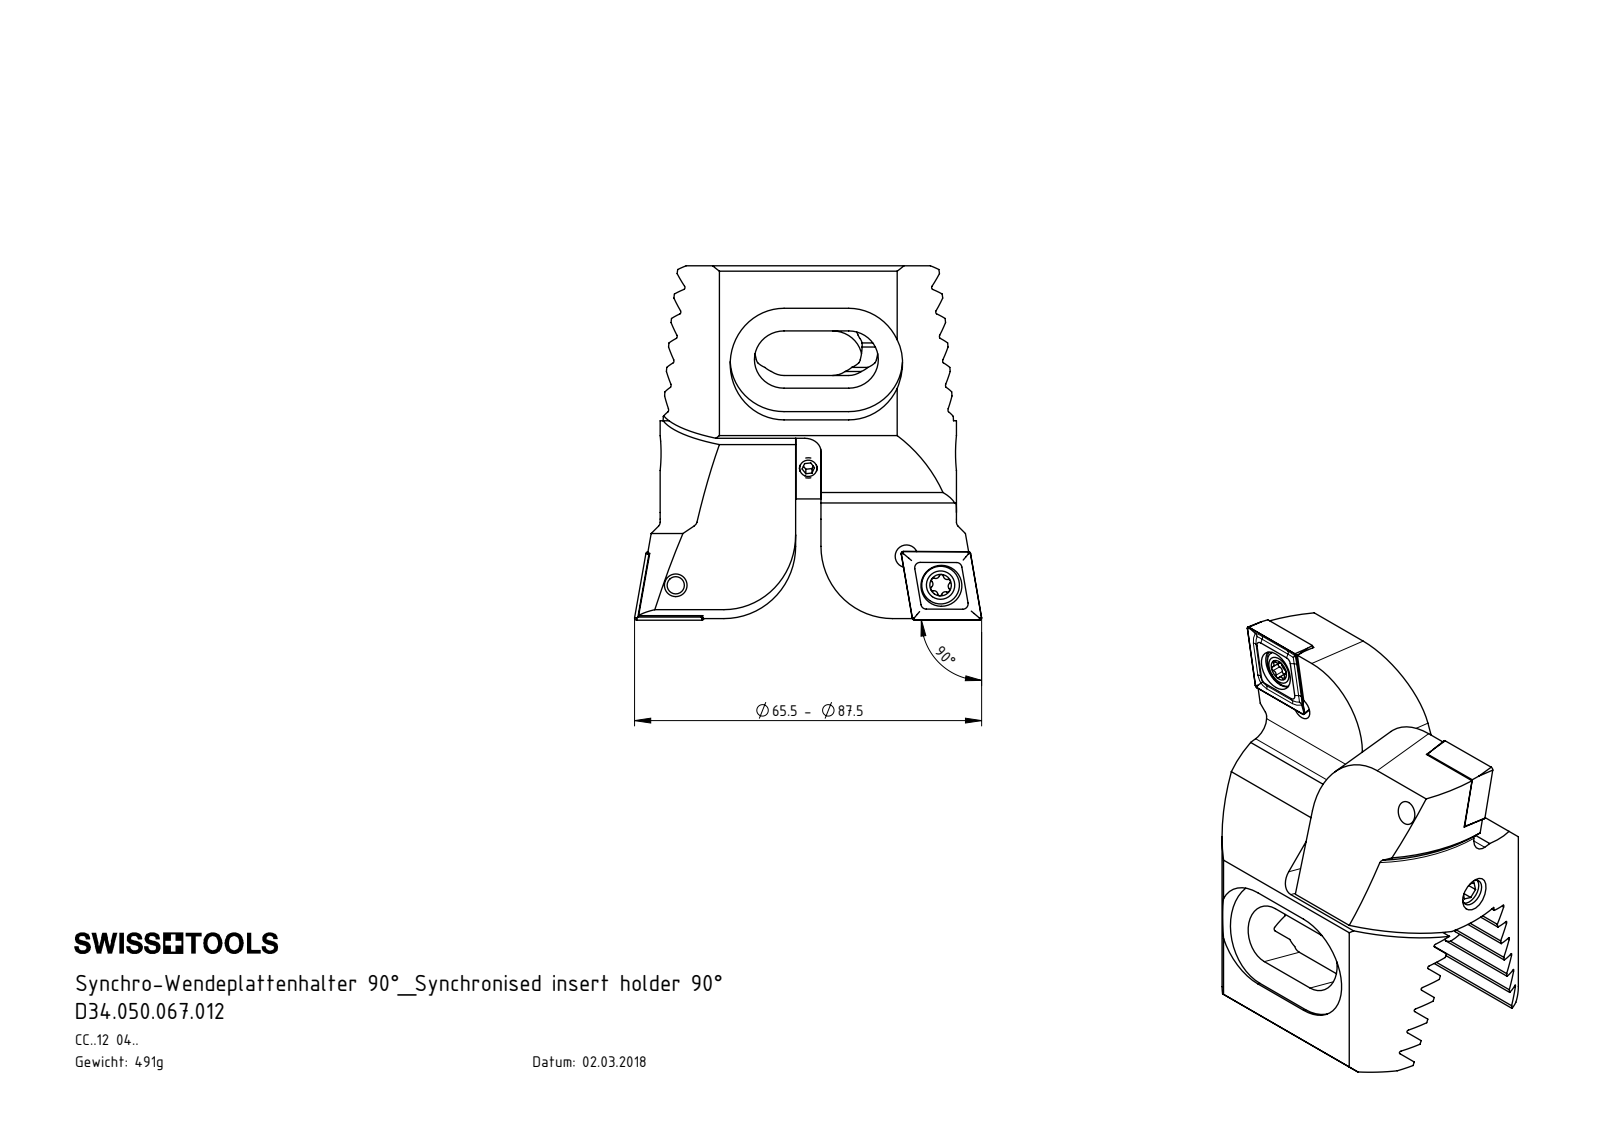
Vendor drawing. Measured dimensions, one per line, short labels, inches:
name: WCC-ER2.001.010_A; Z55-WCC.001.037_A; Z55-ER3.001.052_A; Z55-WCC.003.037_A (+4 more)
written by: SolidWorks 2017 (CONFIG_CONTROL_DESIGN)
unit: in
bodies: 11 solids, 484 faces (187 planar, 155 cylindrical, 142 other)
size: 2.589 × 2.536 × 1.732
volume: 3.818 in³; area: 37.39 in²
holes: 4× ⌀0.165, 3× ⌀0.039, 3× ⌀0.13, 2× ⌀0.217, 2× ⌀0.299, 1× ⌀0.197
bosses: 3× ⌀0.157, 2× ⌀0.276, 2× ⌀0.197, 1× ⌀0.669, 1× ⌀0.236, 1× ⌀0.15
rounds: 12× R0.013, 12× R0.015, 12× R0.027, 8× R0.039, 4× R0.118, 4× R0.217, 4× R0.394, 2× R0.524
face distances: 0.16, 0.32, 0.481, 0.641, 0.801, 0.191, 0.679, 0.039, 0.28, 0.854
hole spacings: 0.326, 0.118, 0.334, 0.335, 0.59, 0.591, 0.602, 1.117
